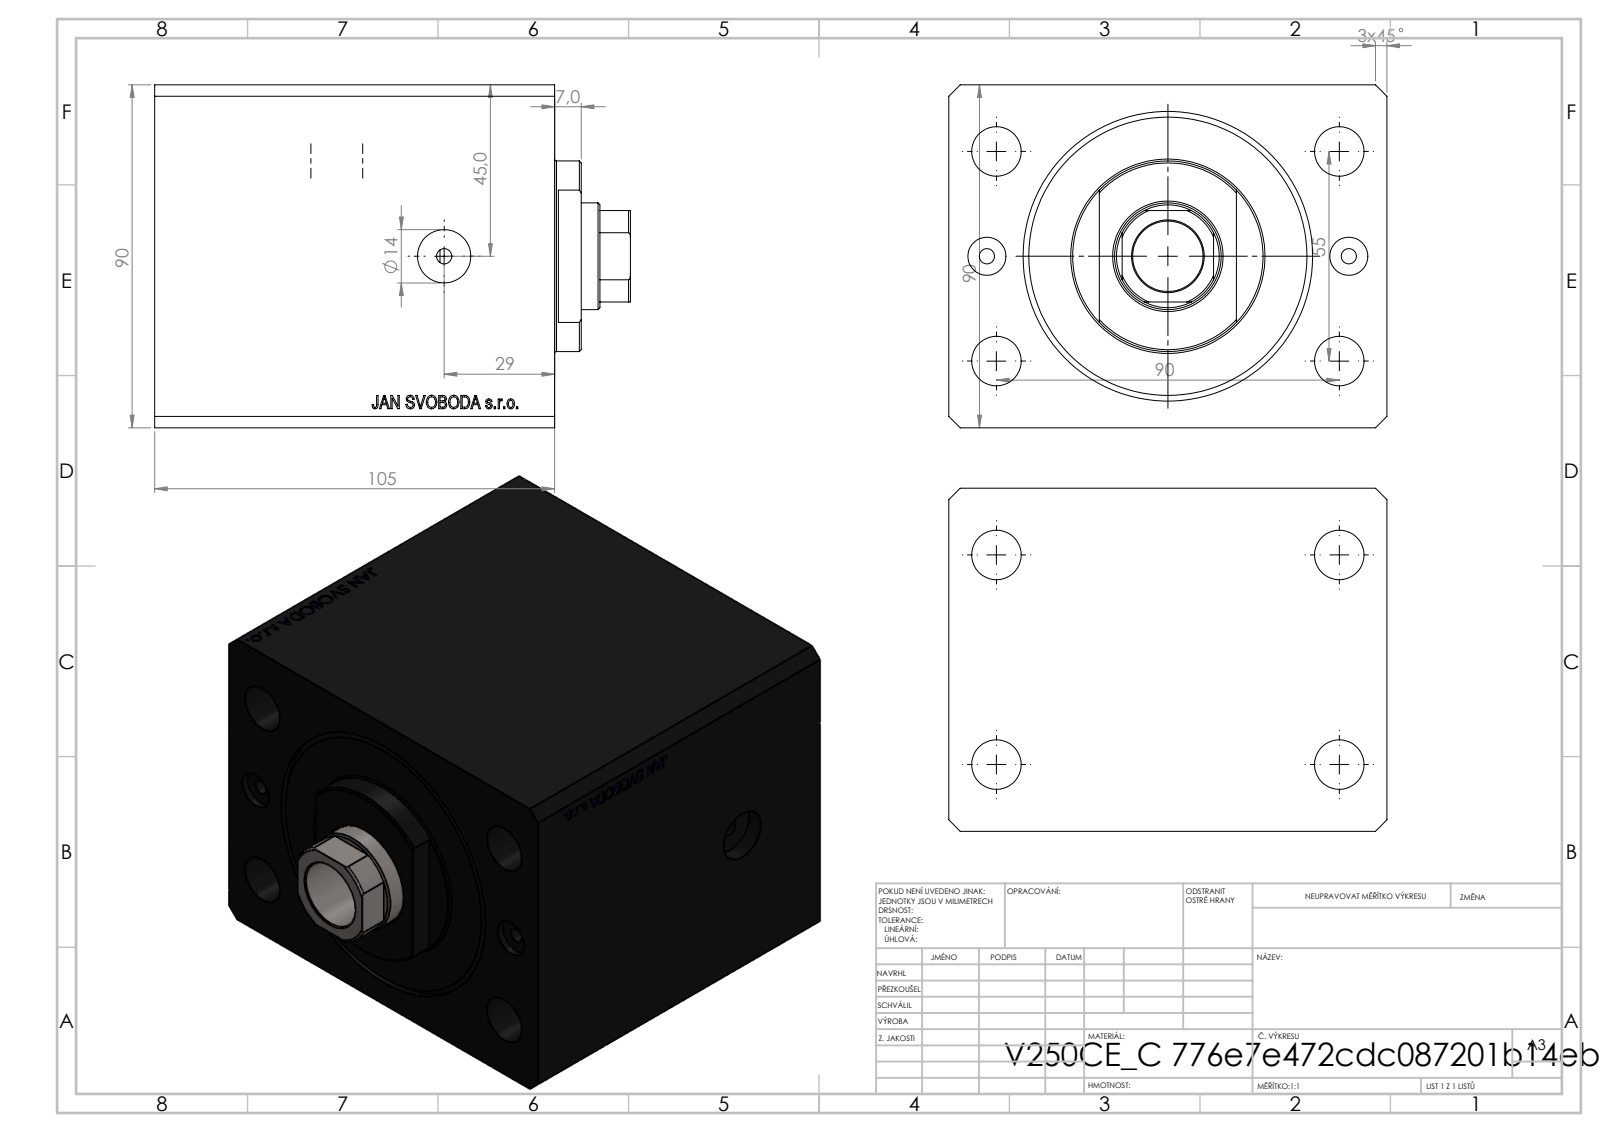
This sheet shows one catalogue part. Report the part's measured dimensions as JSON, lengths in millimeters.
{"part_name": "V250CE_C_Body; V250CE_C_VCP; V250CE_VC_C", "step_written_by": "SolidWorks 2019 (CONFIG_CONTROL_DESIGN)", "units": "millimeters", "bodies": {"solids": 3, "faces": 864, "planar": 428, "cylindrical": 44, "other": 392}, "overall_size": [124.9, 115, 90], "volume_mm3": 985086, "surface_area_mm2": 140555, "round_holes": [[4, 4], [13, 4], [10, 2], [14, 2], [18.5, 1], [28, 1], [63, 1], [76, 1]], "round_bosses_or_shafts": [[50, 1]], "partial_cylinders_radius": [[13.5, 1]], "face_to_face_distances": [90, 115, 105, 17.9, 87.1, 57, 74.9, 30.1, 54.9, 37], "hole_center_spacings": [27.61, 52.74, 96.5, 47.5, 55, 90, 105.48, 47]}
